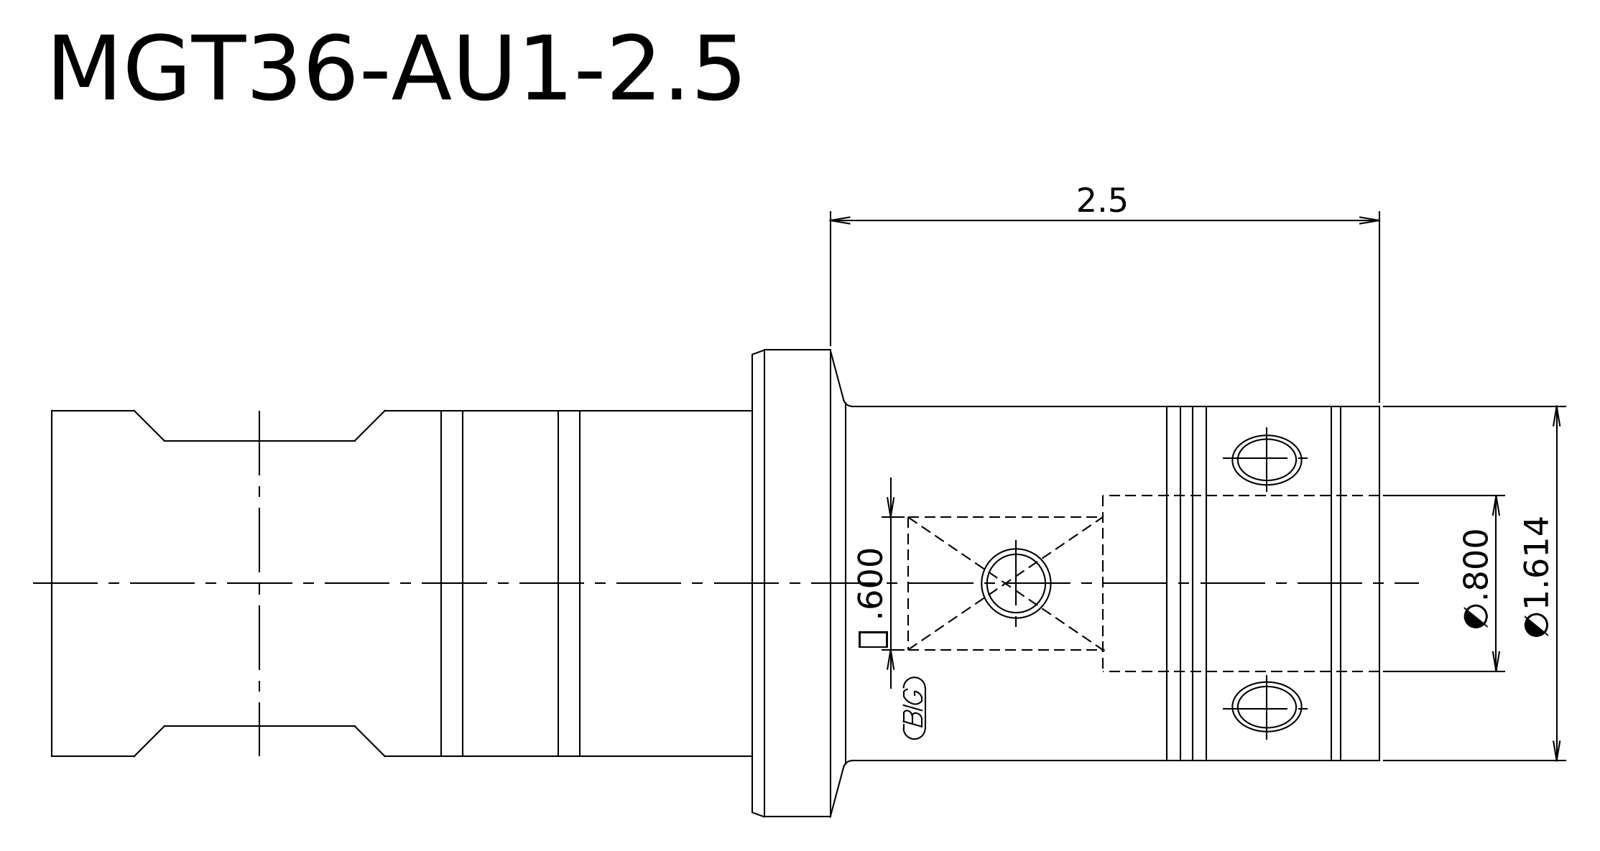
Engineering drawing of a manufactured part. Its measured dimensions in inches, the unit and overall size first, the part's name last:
Units: inches
Overall size (bounding box): 6.043 × 2.126 × 2.126
Round bosses / shafts (diameter × count): ⌀2.126 ×1, ⌀1.614 ×1, ⌀1.575 ×1
Main face-to-face distances: 6.043, 2.854, 3.189
Volume: 12.65 in³ · Surface area: 37.42 in²
Bodies: 1 solid, 8 faces (3 planar, 3 cylindrical, 2 other)
STEP written by: Kubotek KeyCreator 2011 V10.0.2 (22737) (automotive_design)
